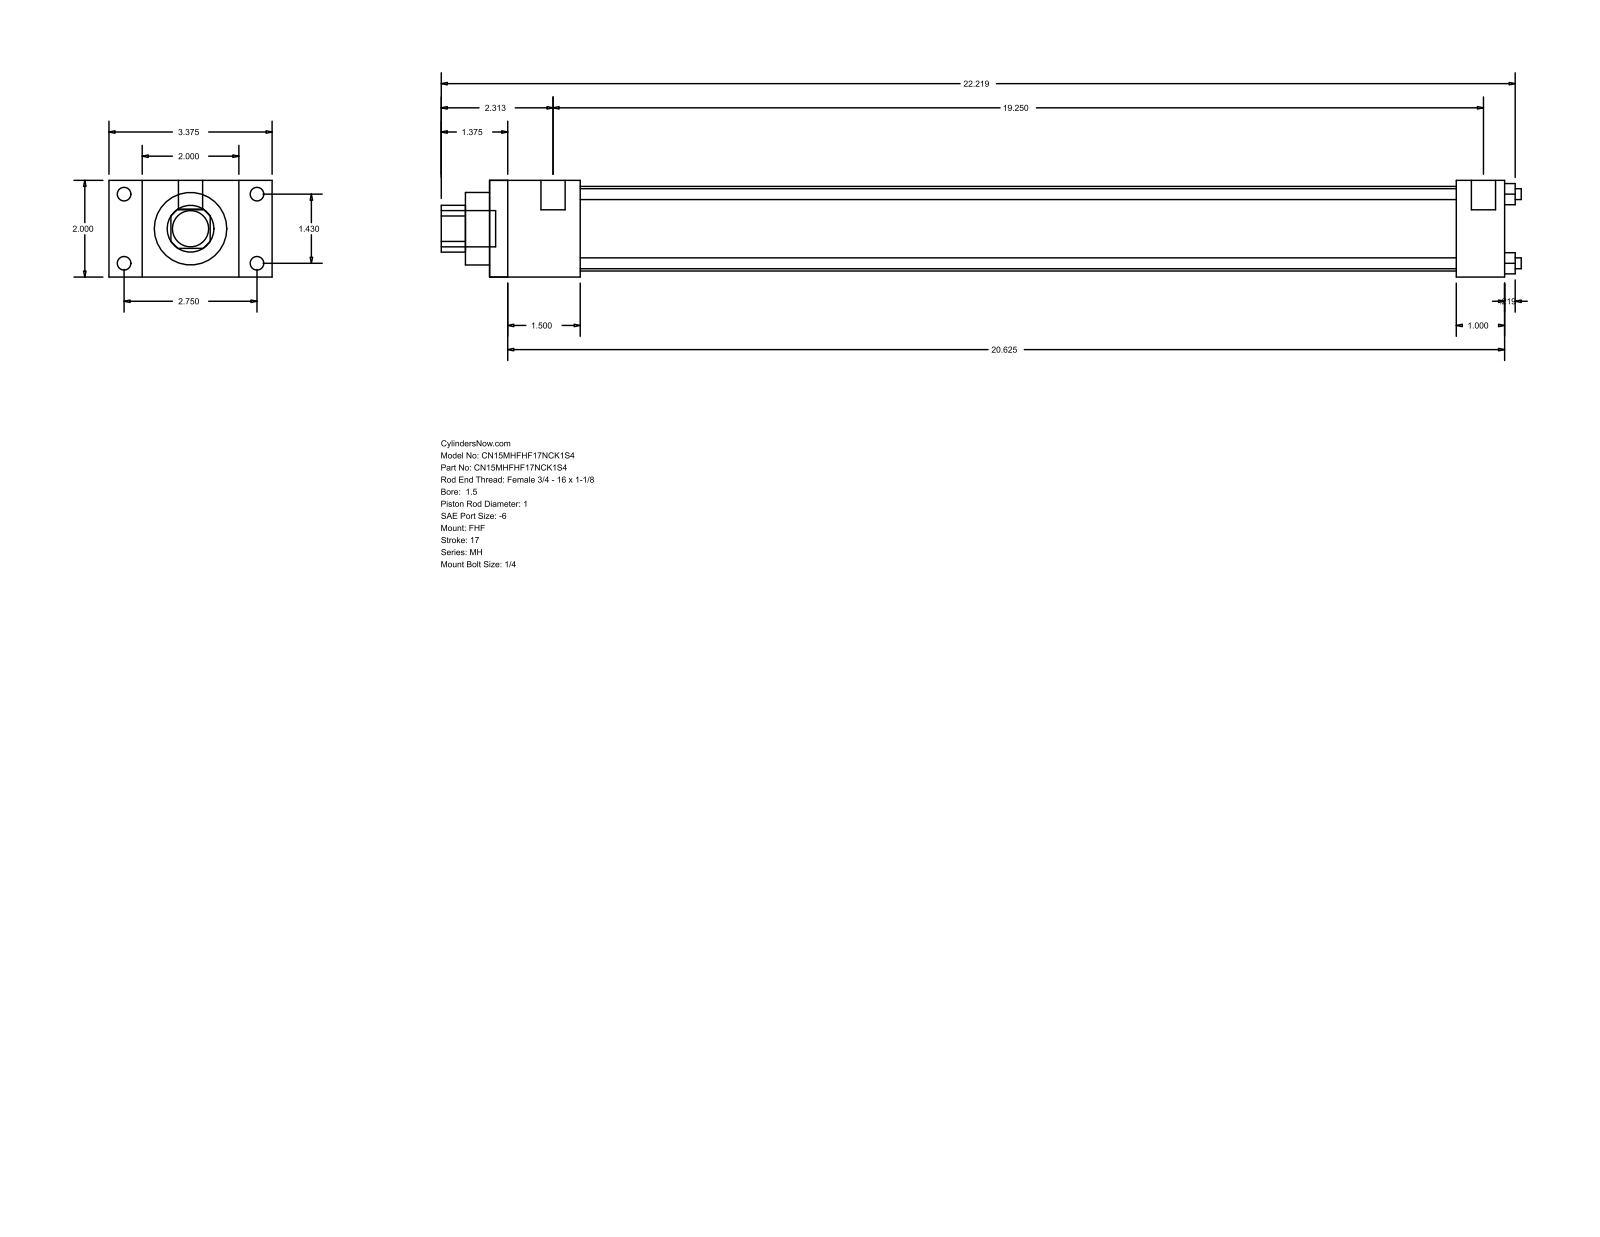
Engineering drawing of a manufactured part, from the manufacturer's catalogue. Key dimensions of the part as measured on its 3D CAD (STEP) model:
Part name (STEP PRODUCT): MH_FHF__0150_1
STEP written by: GSSL Pune (CONFIG_CONTROL_DESIGN)
Units: millimetres
Bodies: 0 solids, 88 faces (60 planar, 28 cylindrical, 0 other)
Overall size (bounding box): 567.53 × 85.72 × 50.8
Round holes (diameter × count): ⌀5.71 ×4, ⌀25.4 ×1, ⌀38.1 ×1, ⌀44.45 ×1
Round bosses / shafts (diameter × count): ⌀7.14 ×4, ⌀5.56 ×4, ⌀12.7 ×2, ⌀19.05 ×1
Partial cylindrical surfaces — rounded edges, fillets, slot ends (radius × count): R12.29 ×1
Main face-to-face distances: 50.8, 17.46, 68.26, 47.63, 85.72, 533.4, 485.77, 25.4, 508, 460.37
Hole centre spacings: 25.68, 36.32, 51.36
